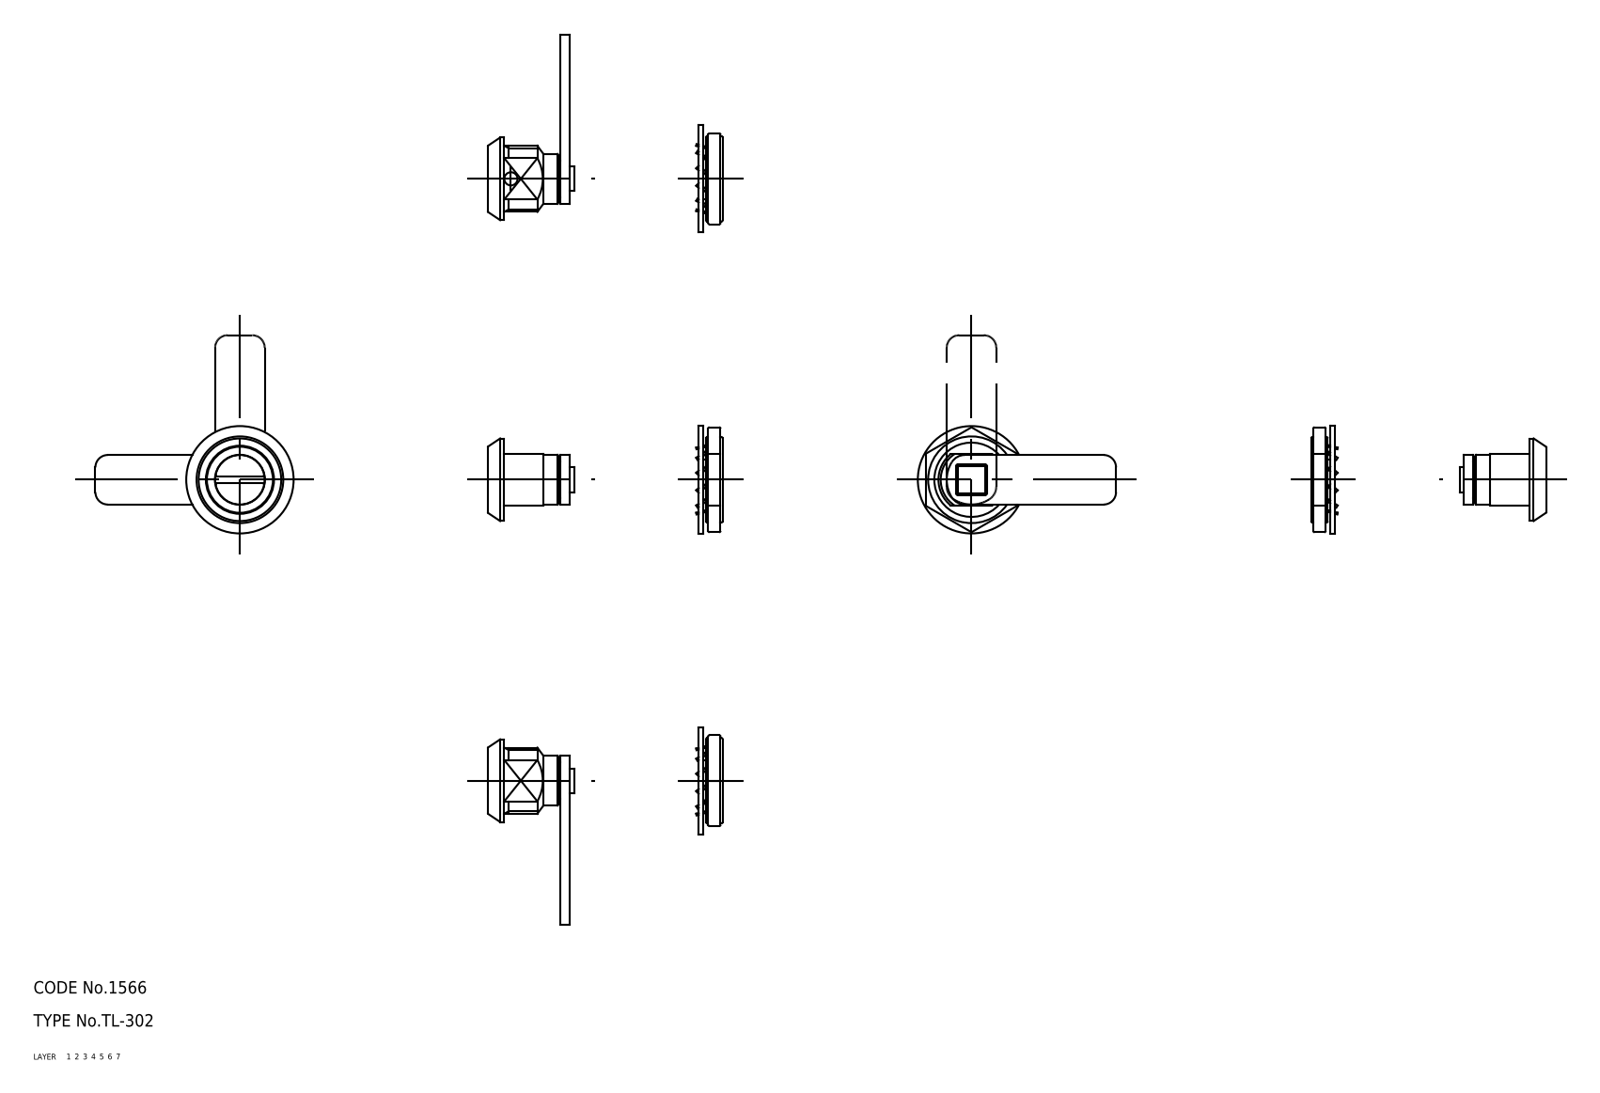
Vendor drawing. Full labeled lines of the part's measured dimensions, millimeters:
Part name (STEP PRODUCT): washer; shaft; nut; cam (+1 more)
STEP written by: CADfix (AUTOMOTIVE_DESIGN)
Units: millimetres
Bodies: 5 solids, 114 faces (0 planar, 0 cylindrical, 114 other)
Overall size (bounding box): 48 × 26 × 20.9
Volume: 5 258 mm³ · Surface area: 5 503 mm²
